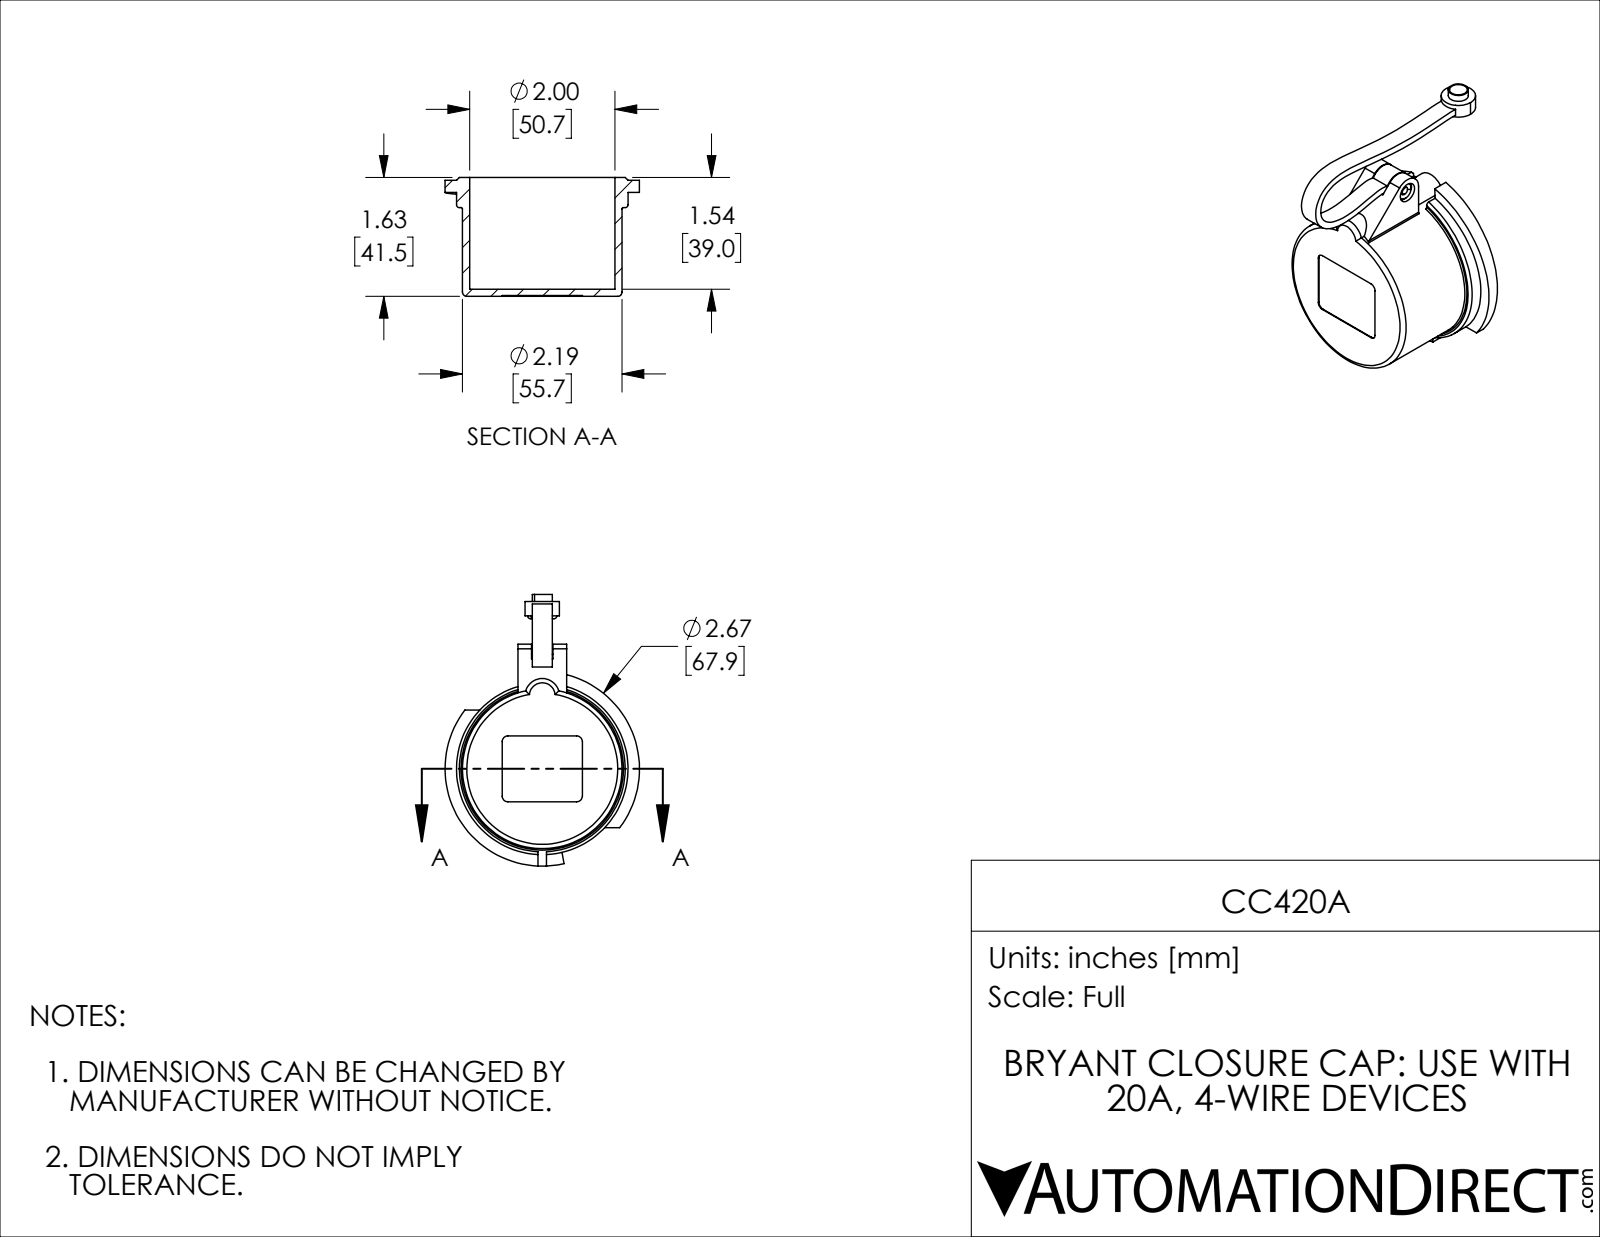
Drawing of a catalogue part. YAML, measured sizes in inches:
part_name: "CC420A"
step_written_by: "SolidWorks 2021 (CONFIG_CONTROL_DESIGN)"
units: inches
bodies: {solids: 2, faces: 116, planar: 41, cylindrical: 52, other: 23}
overall_size: [3.734, 3.149, 2.673]
volume: 2.08
surface_area: 39.41
round_holes:
  - {diameter: 0.118, count: 1}
  - {diameter: 0.169, count: 1}
  - {diameter: 0.197, count: 1}
  - {diameter: 0.244, count: 1}
  - {diameter: 0.276, count: 1}
  - {diameter: 1.996, count: 1}
round_bosses_or_shafts:
  - {diameter: 2.358, count: 1}
  - {diameter: 2.193, count: 1}
  - {diameter: 0.472, count: 1}
  - {diameter: 0.433, count: 1}
  - {diameter: 0.276, count: 1}
  - {diameter: 0.236, count: 1}
  - {diameter: 0.157, count: 1}
partial_cylinders:
  - {radius: 0.079, count: 4}
  - {radius: 0.02, count: 2}
  - {radius: 0.138, count: 1}
  - {radius: 0.236, count: 1}
  - {radius: 1.337, count: 1}
face_to_face_distances: [0.098, 0.087, 1.634, 1.622, 1.535, 1.594, 1.583, 1.496, 0.039, 0.197]
